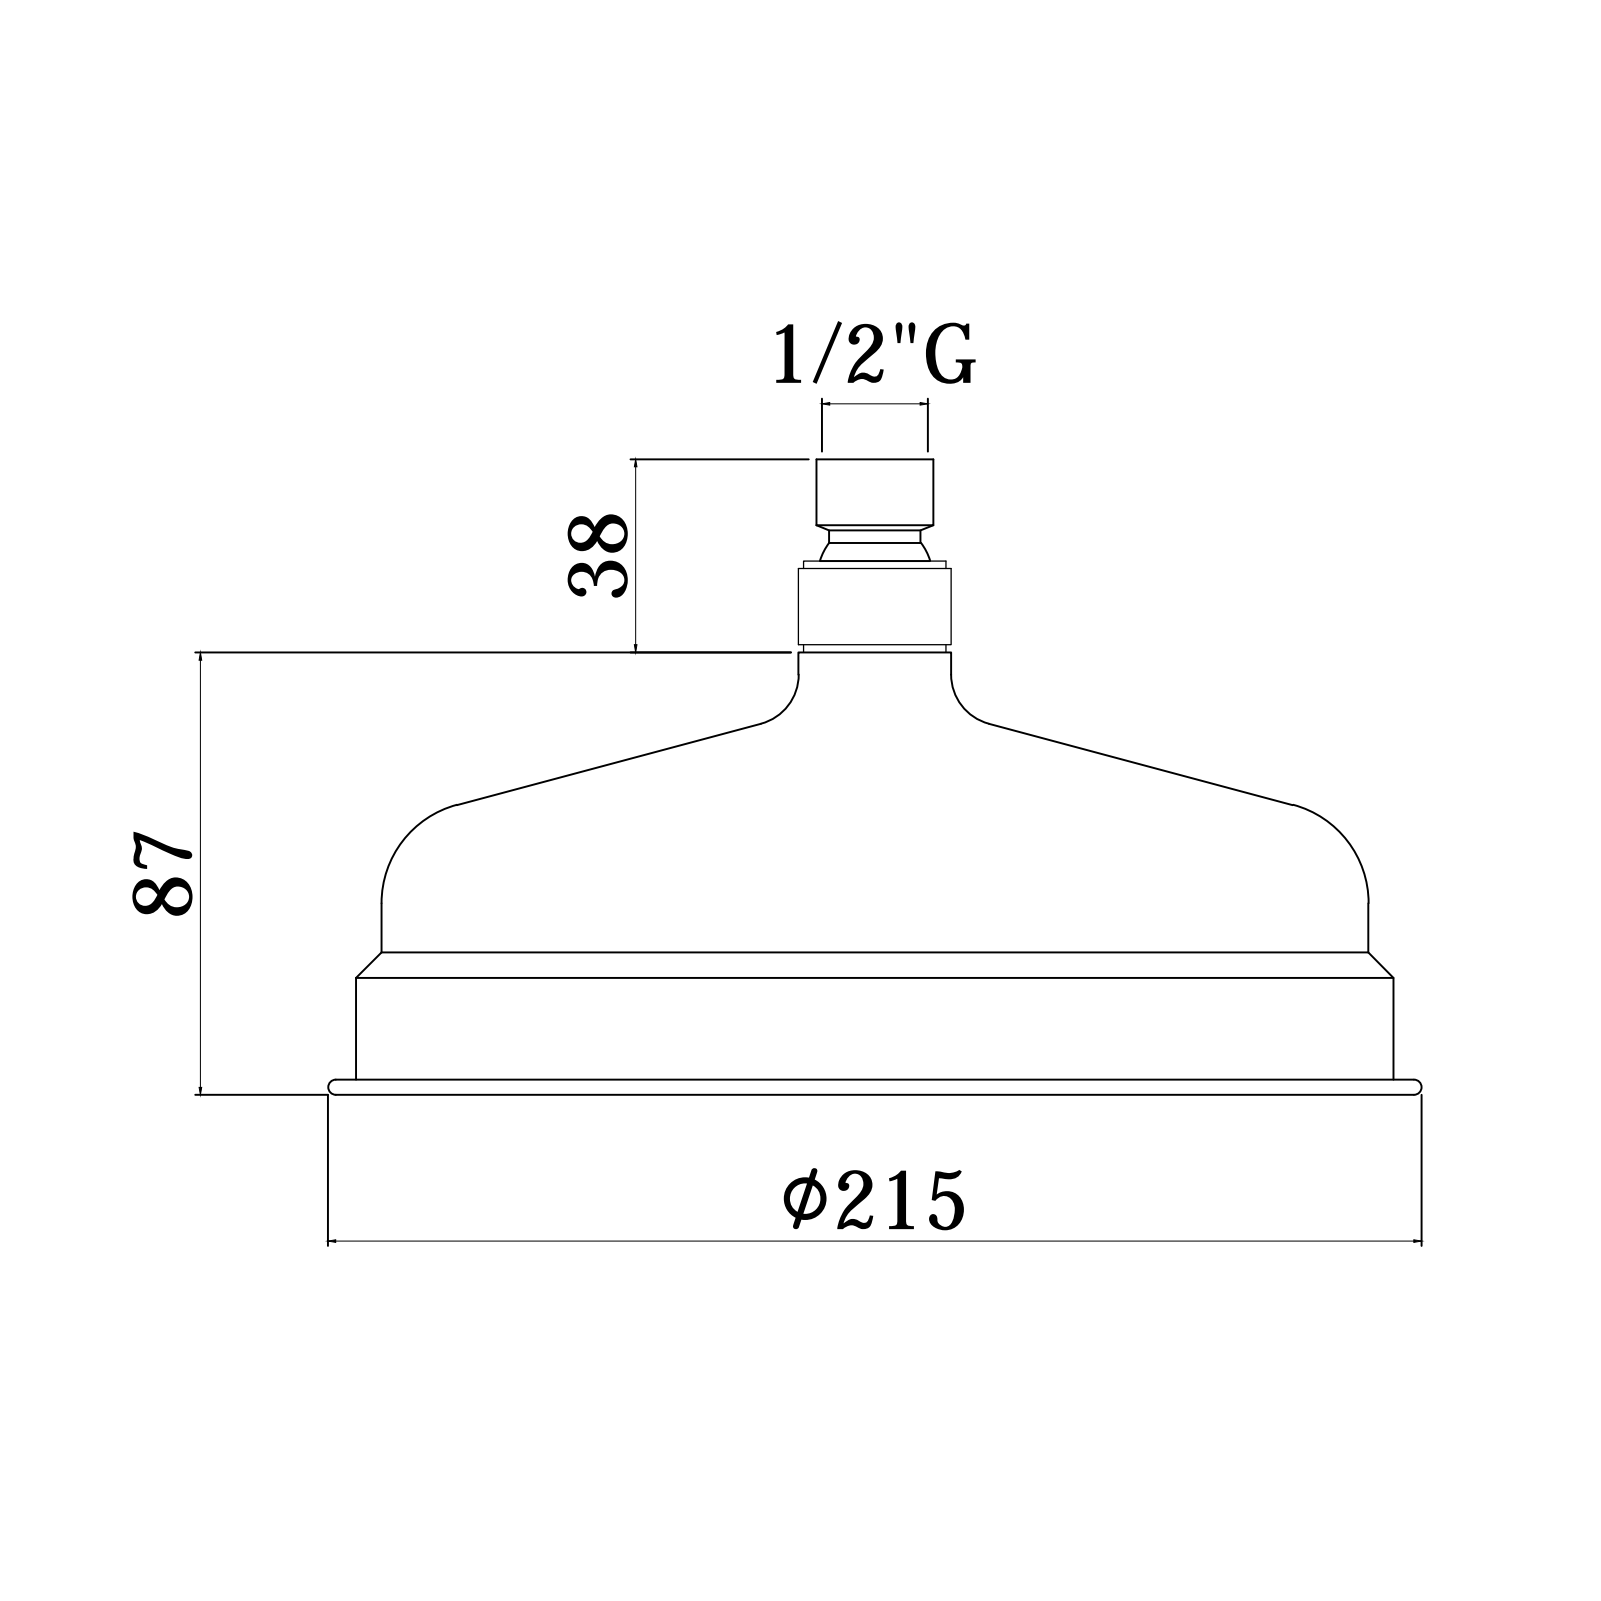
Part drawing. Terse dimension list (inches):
name: ZSOF046CR
written by: CREO PARAMETRIC BY PTC INC, 2020044 (CONFIG_CONTROL_DESIGN)
unit: in
bodies: 1 solid, 690 faces (226 planar, 234 cylindrical, 230 other)
size: 8.465 × 8.465 × 4.744
volume: 83.54 in³; area: 179.6 in²
holes: 100× ⌀0.079, 1× ⌀0.276, 1× ⌀0.551, 1× ⌀0.748, 1× ⌀7.48
bosses: 1× ⌀8.327, 1× ⌀8.071, 1× ⌀1.22, 1× ⌀1.181, 1× ⌀1.142, 1× ⌀1.102, 1× ⌀0.906, 1× ⌀0.677
rounds: 1× R0.266
face distances: 0.591, 2.756, 2.165, 4.094, 3.504, 1.339, 0.906, 0.65, 4.299, 3.709
hole spacings: 2.244, 2.795, 2.693, 1.454, 2.646, 2.751, 4.347, 1.142
